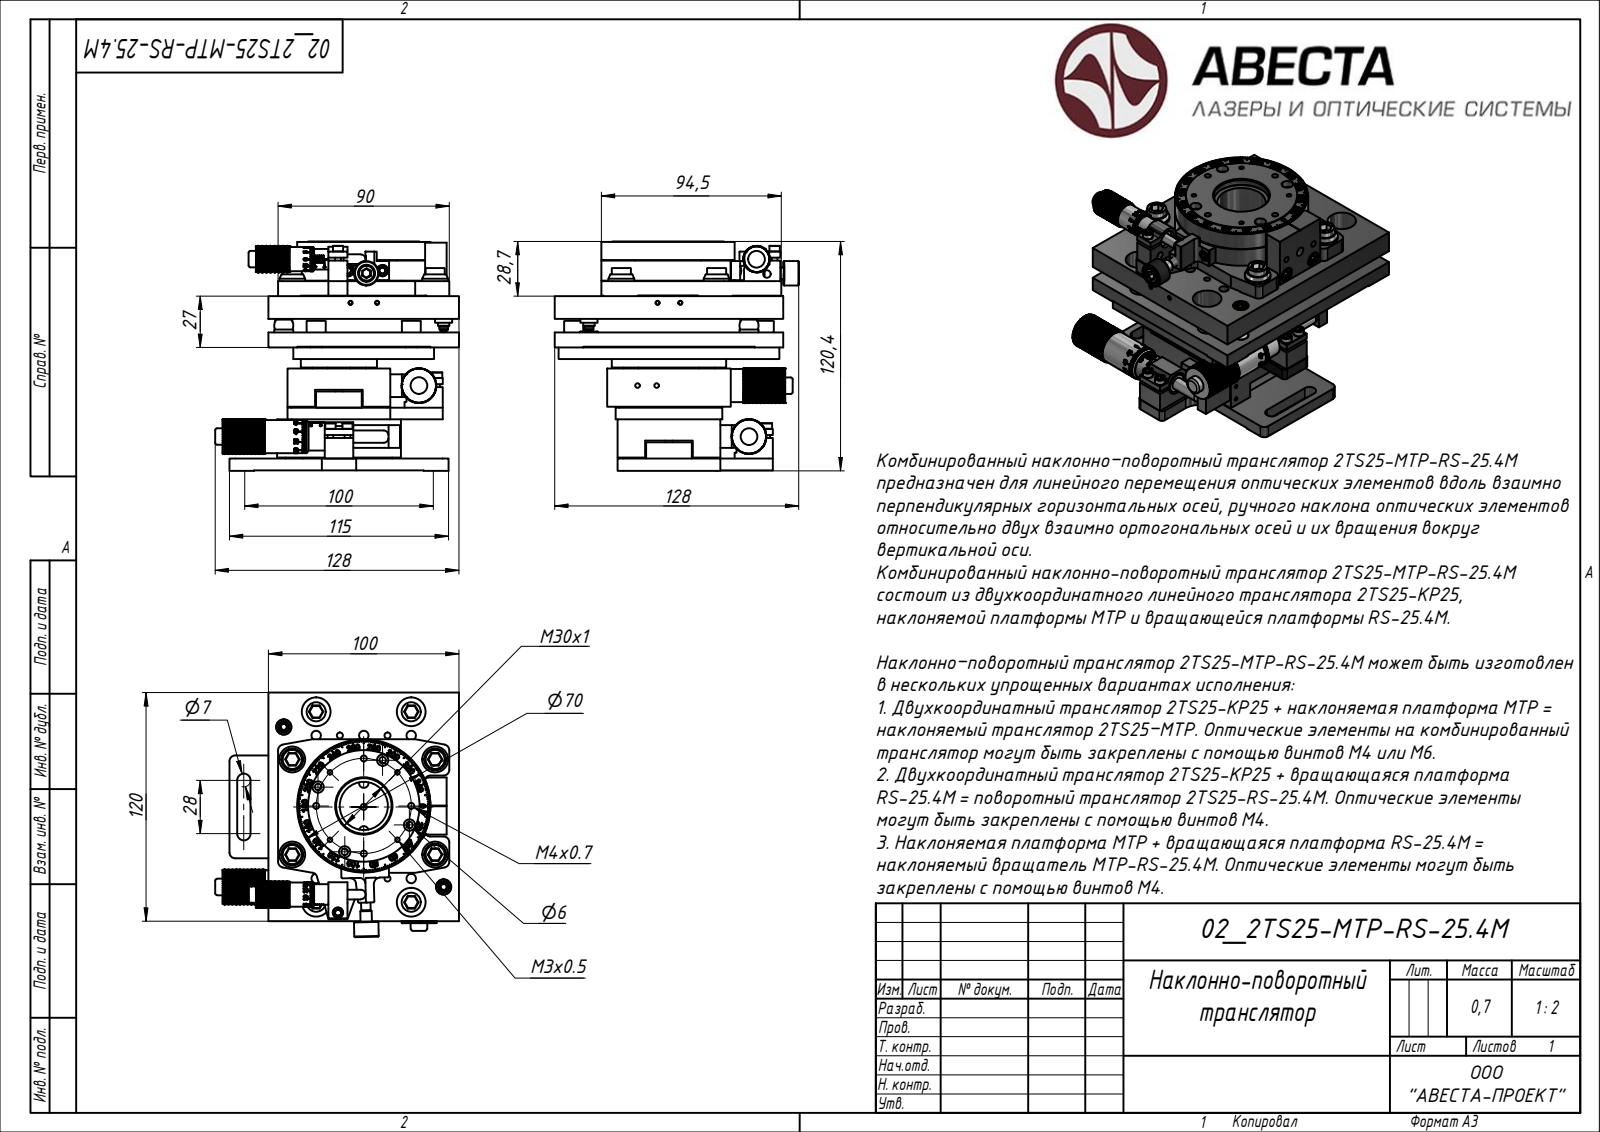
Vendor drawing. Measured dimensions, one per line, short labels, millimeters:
written by: Rhino 7.34 (AUTOMOTIVE_DESIGN)
unit: mm
bodies: 1338 solids, 17936 faces (14847 planar, 1511 cylindrical, 1578 other)
size: 128.31 × 128 × 120.4
volume: 622 383 mm³; area: 259 738 mm²
holes: 43× ⌀2.46, 35× ⌀6, 29× ⌀3.24, 15× ⌀3.5, 15× ⌀4.92, 11× ⌀2.46, 10× ⌀3.4, 10× ⌀5, 10× ⌀6.5, 8× ⌀3.2, 7× ⌀2.01, 6× ⌀2.8
bosses: 30× ⌀5.4, 30× ⌀3, 10× ⌀10, 9× ⌀6, 8× ⌀2.5, 7× ⌀2, 6× ⌀4.5, 6× ⌀4
rounds: 19× R3, 10× R2, 9× R0.64, 8× R3.25, 7× R0.5, 7× R1.23, 6× R1.1, 6× R1.23
face distances: 26.7, 7, 6.5, 19, 14, 0.5, 25.5, 7.5, 26.5, 12
hole spacings: 15.5, 10, 25, 28.35, 42.41, 50.02, 9.11, 19.14
